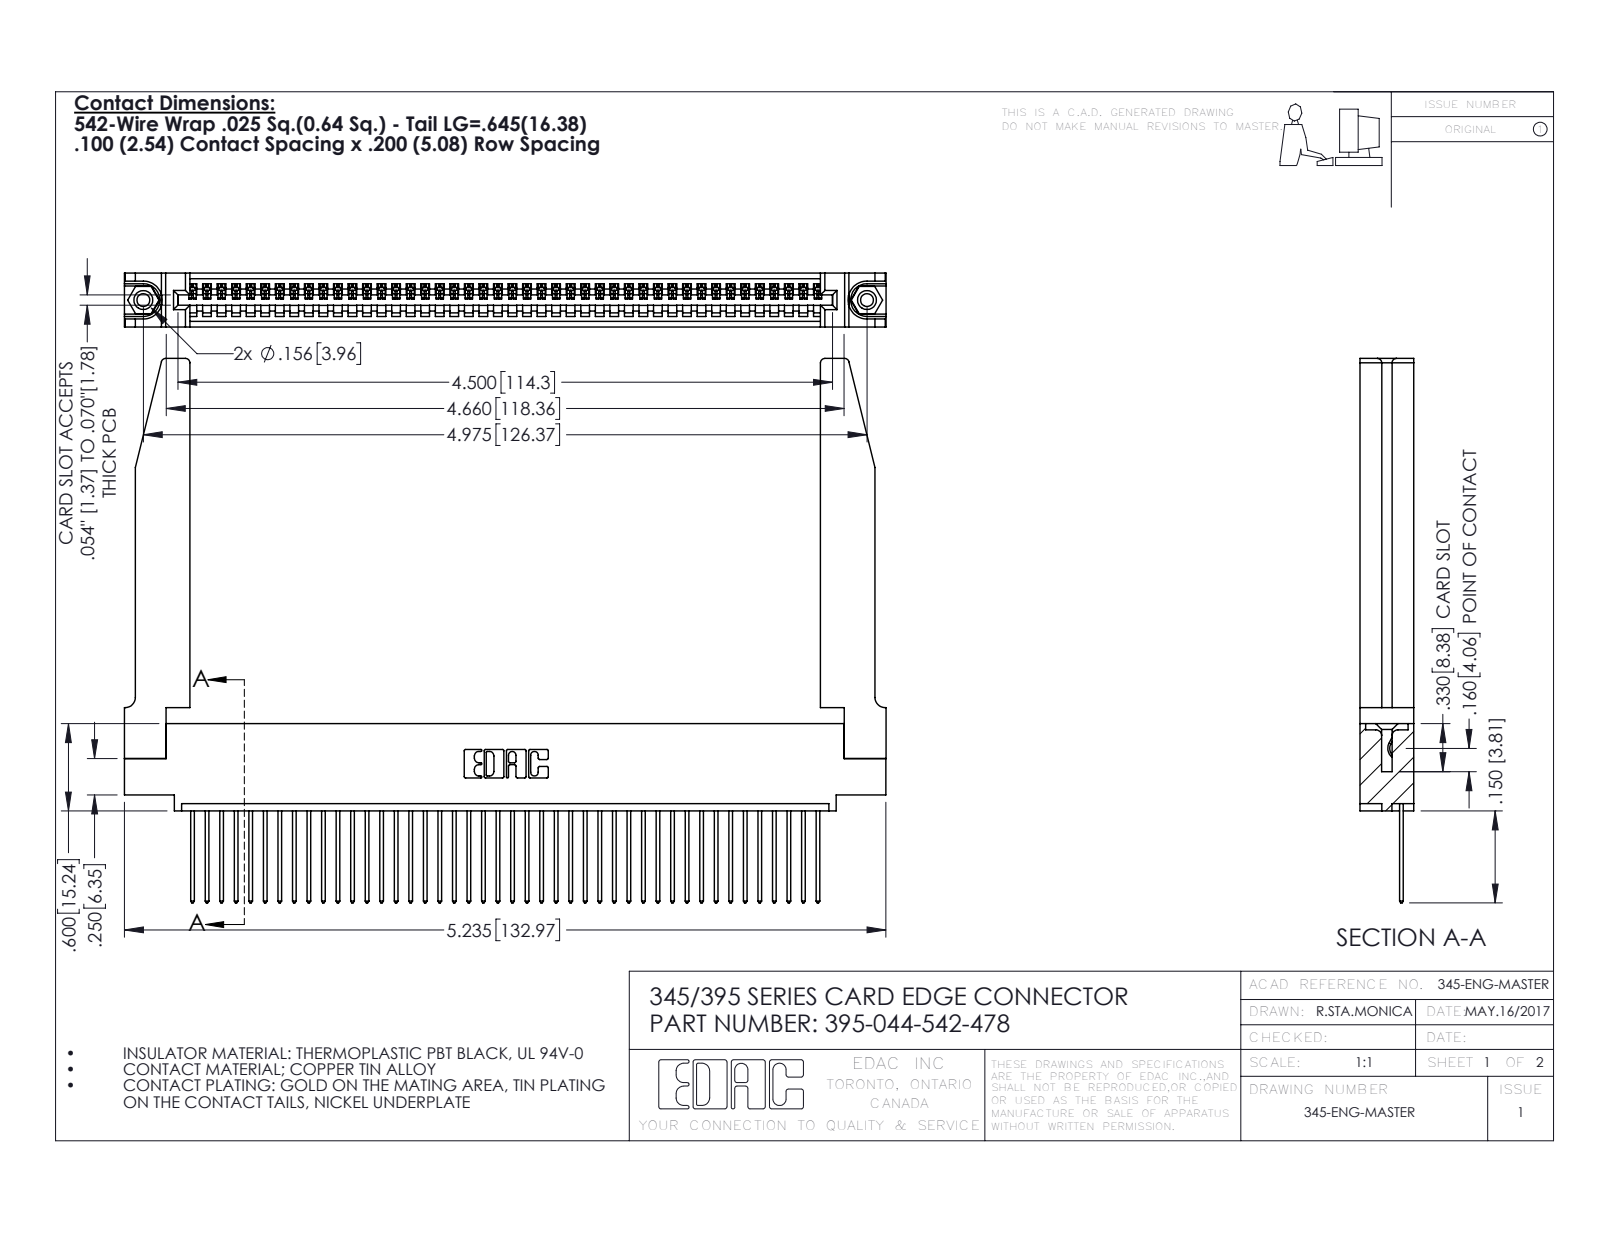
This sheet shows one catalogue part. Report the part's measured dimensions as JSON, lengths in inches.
{"part_name": "345-292-001_345-293-142; 395-044-542-478; 345 Part_0.110 Offset - 0.156 Dia-TH; 345-250-001_345-250-001-102 (+1 more)", "step_written_by": "SolidWorks 2016 (CONFIG_CONTROL_DESIGN)", "units": "inches", "bodies": {"solids": 49, "faces": 2916, "planar": 1986, "cylindrical": 878, "other": 52}, "overall_size": [5.236, 3.742, 0.37], "volume_in3": 1.248, "surface_area_in2": 37.84, "round_holes": [[0.089, 2], [0.125, 2], [0.156, 2], [0.064, 1]], "round_bosses_or_shafts": [[0.155, 2]], "partial_cylinders_radius": [[0.006, 88], [0.01, 88], [0.01, 22], [0.03, 8], [0.007, 6], [0.031, 6], [0.026, 3], [0.031, 2]], "face_to_face_distances": [0.072, 0.37, 0.298, 0.098, 0.272, 0.025, 0.2, 0.225, 0.148, 0.15], "hole_center_spacings": [0.27, 4.739, 4.975]}
